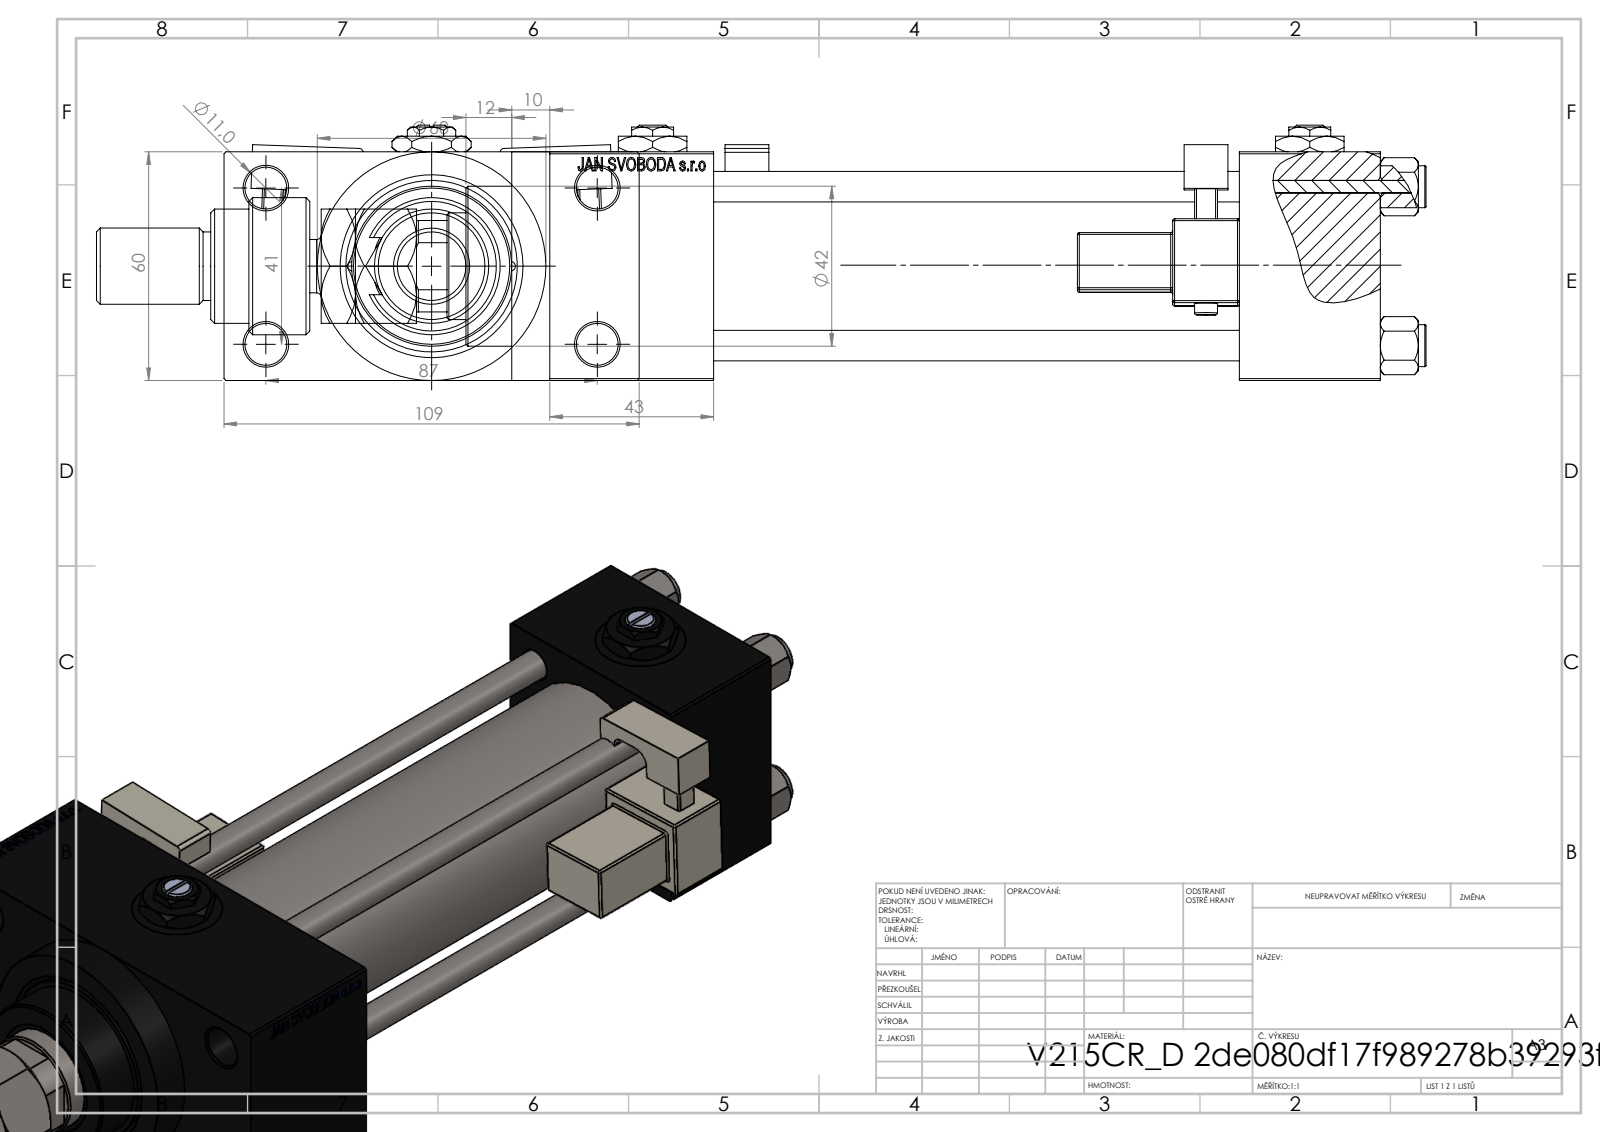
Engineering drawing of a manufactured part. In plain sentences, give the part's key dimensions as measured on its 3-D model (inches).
The part is named "NUT_M5_D; V215CR_VCP_D; V215CR_MSU; V215CR_D_Body (+5 more)". Its 3-D file was written by "SolidWorks 2019 (CONFIG_CONTROL_DESIGN)". It is 17 solids with 1454 faces: 636 planar, 176 cylindrical and 642 other. Overall it measures 13.74 by 4.291 by 2.638 inches. Its volume is 43.57 cubic inches and its surface area 300.3 square inches. Round holes: 4 of diameter 0.315, 4 of diameter 0.433, 4 of diameter 0.656, 4 of diameter 0.945, 3 of diameter 0.276, 2 of diameter 0.098, 1 of diameter 0.728, 1 of diameter 1.102, 1 of diameter 1.22, 1 of diameter 1.575, 1 of diameter 1.772. Round bosses or shafts: 4 of diameter 0.433, 2 of diameter 0.236, 1 of diameter 2.362, 1 of diameter 1.811, 1 of diameter 1.654, 1 of diameter 1.417, 1 of diameter 1.181, 1 of diameter 0.866. Partial cylindrical surfaces (rounded edges, fillets, slot ends): 48 of radius 0.02, 2 of radius 0.039, 2 of radius 0.098, 2 of radius 0.157, 1 of radius 0.295, 1 of radius 0.472, 1 of radius 0.531. The main face-to-face distances are 2.362, 5.433, 0.965, 3.327, 1.457, 6.89, 1.693, 8.583, 7.126, 4.291. The hole center spacings are 0.821, 0.892, 1.161, 1.206, 1.642, 1.832, 1.856, 1.893.
